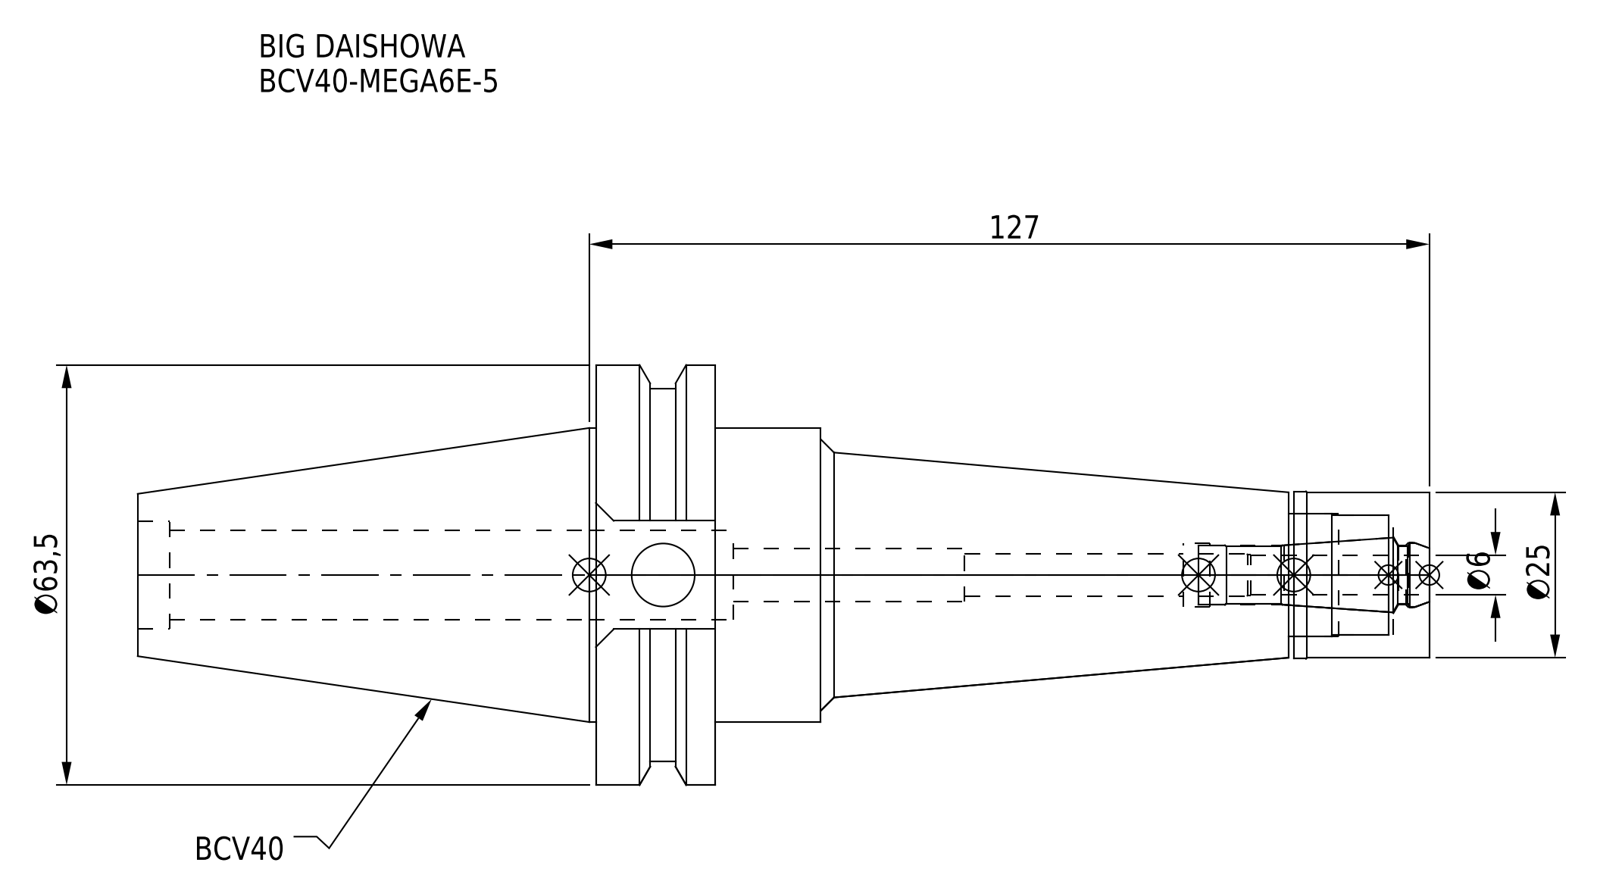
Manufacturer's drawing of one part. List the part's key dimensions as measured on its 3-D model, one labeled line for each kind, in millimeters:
Part name (STEP PRODUCT): DXF_TEMP_ASSY_ASM_4_ASM.stp; BCV40-MEGA6E-5-060-FreeParts; BCV40ME06050-006_ASM.stp; BCV40-MEGA6E-5-060.stp (+3 more)
STEP written by: SolidWorks 2019 (CONFIG_CONTROL_DESIGN)
Units: millimetres
Bodies: 2 solids, 93 faces (31 planar, 42 cylindrical, 20 other)
Overall size (bounding box): 195.25 × 63.5 × 61.35
Volume: 187 743 mm³ · Surface area: 36 096 mm²
Round holes (diameter × count): ⌀6.4 ×1, ⌀8 ×1, ⌀9 ×1, ⌀9.53 ×1, ⌀9.6 ×1, ⌀9.9 ×1, ⌀13.6 ×1, ⌀16.32 ×1, ⌀18 ×1, ⌀18.5 ×1
Round bosses / shafts (diameter × count): ⌀63.5 ×1, ⌀56.36 ×1, ⌀44.45 ×1, ⌀25.3 ×1, ⌀25 ×1
Main face-to-face distances: 18.05, 107.95, 126, 195.25, 87.3, 69.25, 20.5, 87.45, 105.5, 174.75
